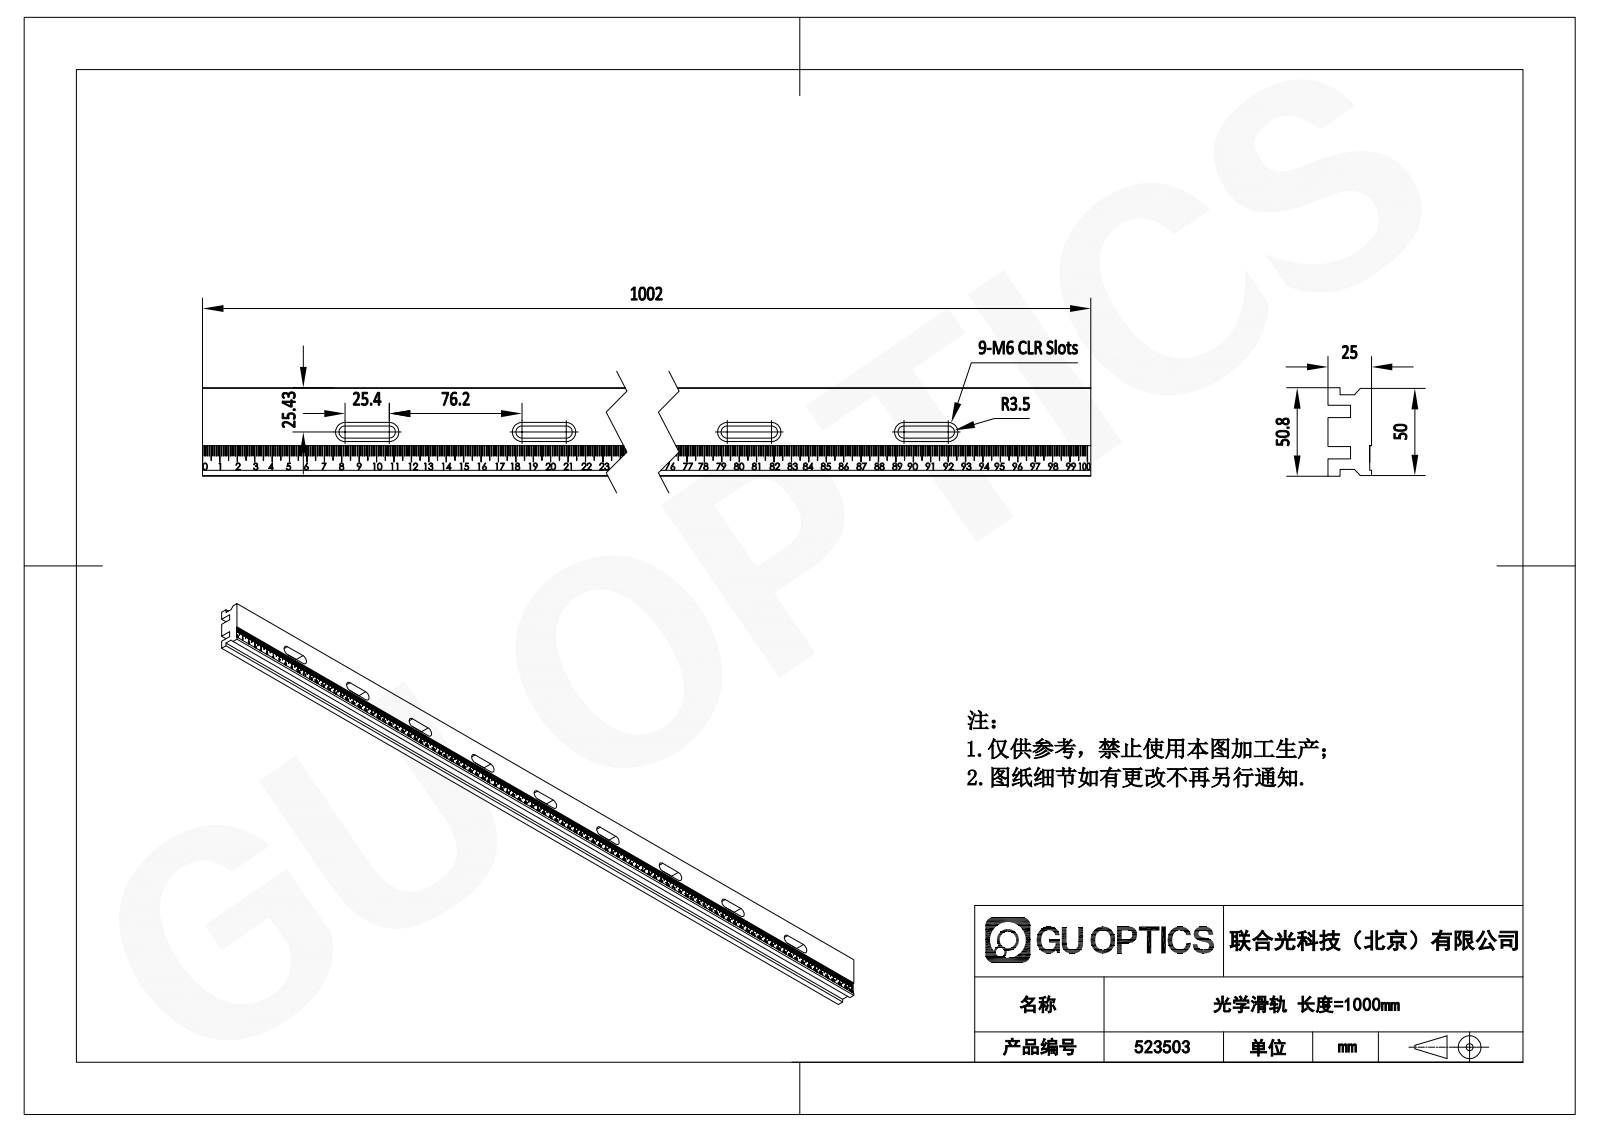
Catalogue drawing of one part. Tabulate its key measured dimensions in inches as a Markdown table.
| quantity | value |
| --- | --- |
| part name | ORL-100 |
| STEP written by | SolidWorks 2012 (CONFIG_CONTROL_DESIGN) |
| units | inches |
| bodies | 1 solid, 6709 faces (5305 planar, 36 cylindrical, 1368 other) |
| overall size | 39.449 × 2 × 0.984 |
| volume | 56.31 in³ |
| surface area | 359.6 in² |
| partial cylindrical surfaces (radius × count) | 0.138 × 18, 0.217 × 18 |
| main face-to-face distances | 0.984, 0.28, 0.933, 0.236, 0.433, 0.516, 1.169, 1.449, 0.039, 0.394 |
